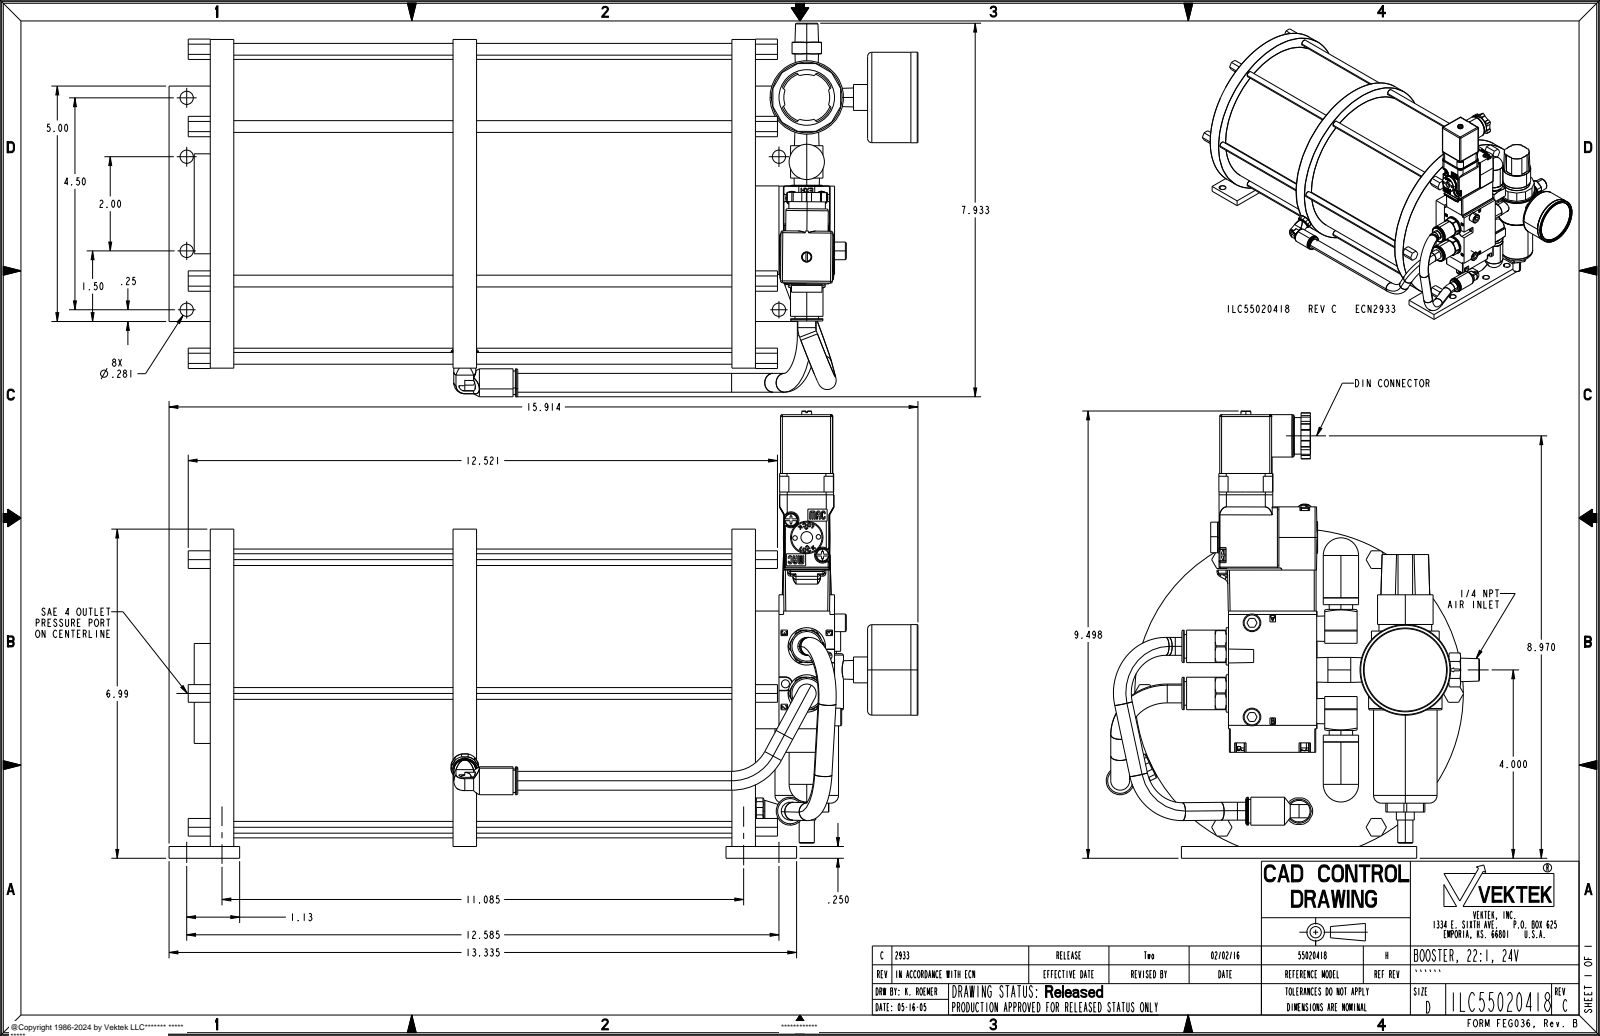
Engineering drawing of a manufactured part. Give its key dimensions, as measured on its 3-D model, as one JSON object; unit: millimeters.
{"part_name": "ILC55020418", "step_written_by": "PRO/ENGINEER BY PARAMETRIC TECHNOLOGY CORPORATION, 2013320 (CONFIG_CONTROL_DESIGN)", "units": "millimeters", "bodies": {"solids": 1, "faces": 1437, "planar": 695, "cylindrical": 424, "other": 318}, "overall_size": [404.2, 241.2, 201.5], "volume_mm3": 5981000, "surface_area_mm2": 389400, "round_holes": [[7.1, 12], [5.1, 4], [5.4, 2], [6.7, 2], [7, 2], [9.5, 2], [12.7, 2], [13.7, 2], [16.5, 2], [17.5, 2], [20.2, 2], [3.7, 1]], "round_bosses_or_shafts": [[6.4, 12], [9.7, 6], [14.7, 5], [10.2, 4], [9.5, 4], [11.7, 3], [15.1, 2], [12.7, 2]], "partial_cylinders_radius": [[1, 20], [0.3, 14], [0.2, 13], [0.8, 13], [4, 12], [0.5, 11], [1.1, 8], [1, 6]], "face_to_face_distances": [294.3, 12.7, 281.6, 131, 150.5, 6.4, 163.2, 143.7, 118.3, 268.9], "hole_center_spacings": [50.8, 19.1, 31.8, 37, 54.3, 82.6, 84.7, 300.6]}
